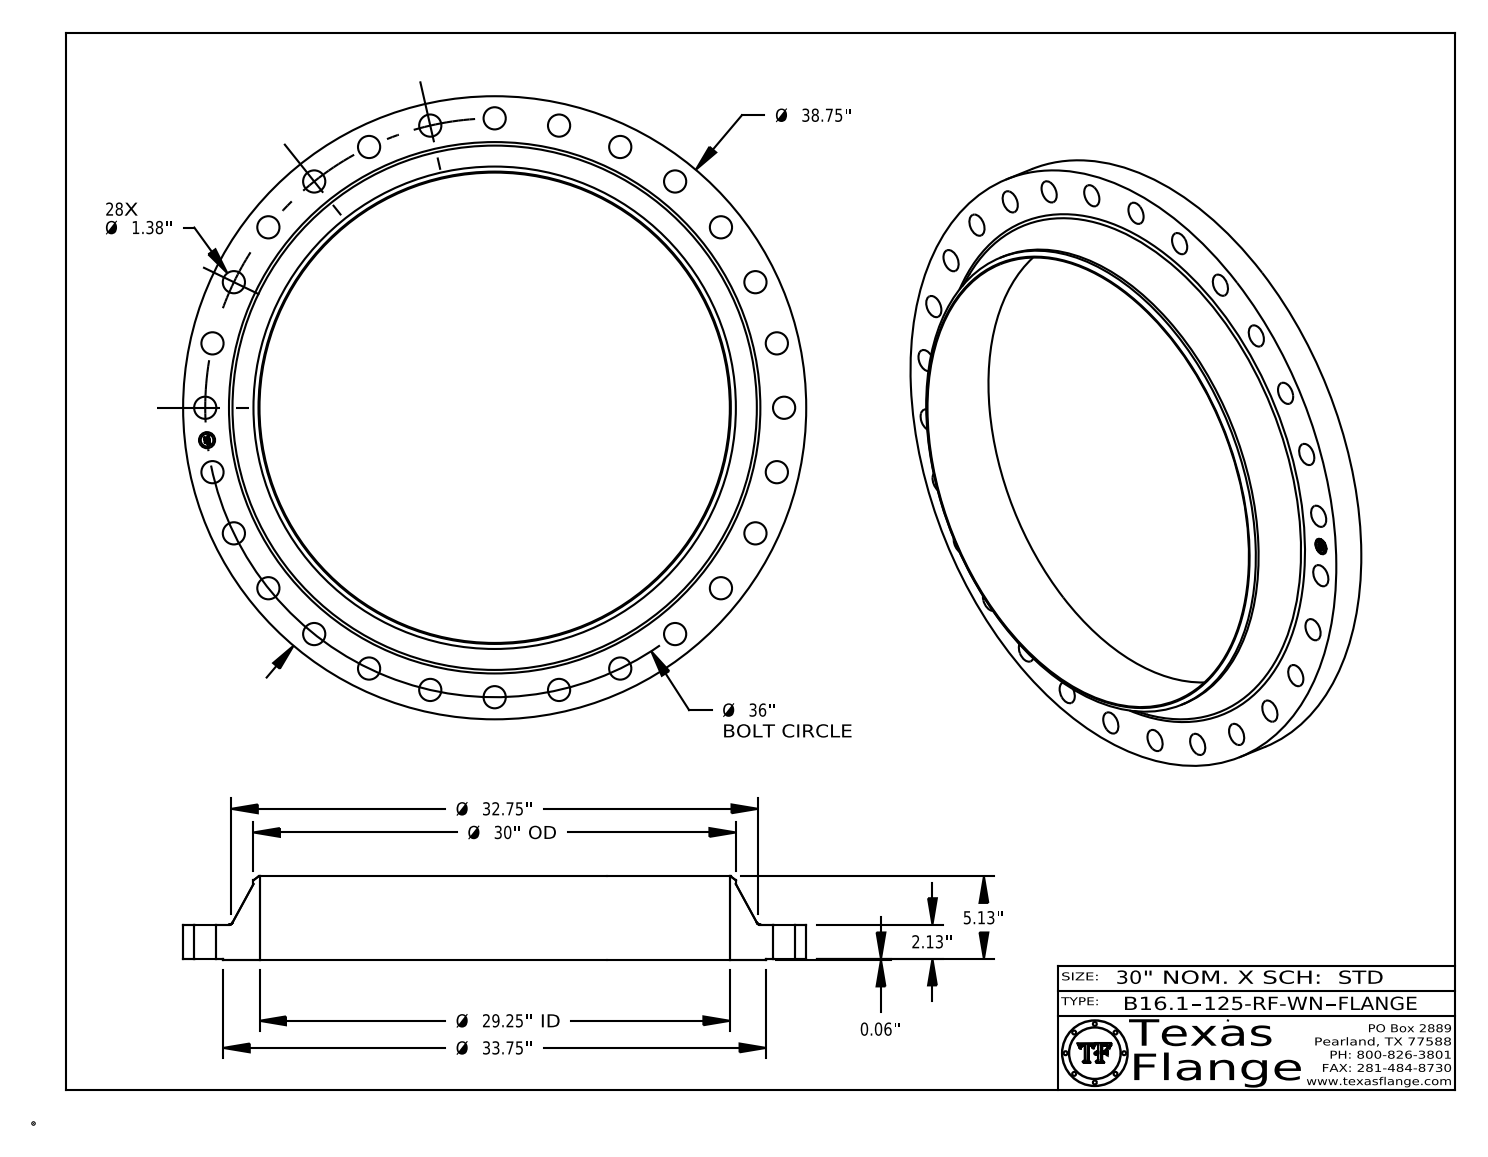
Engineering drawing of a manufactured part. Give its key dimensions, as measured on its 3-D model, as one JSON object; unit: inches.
{"part_name": "B16.1, Class 125-RF-WN", "step_written_by": "CATIA V5 STEP AP214 (AUTOMOTIVE_DESIGN)", "units": "inches", "bodies": {"solids": 1, "faces": 459, "planar": 369, "cylindrical": 84, "other": 6}, "overall_size": [38.75, 38.75, 5.193], "volume_in3": 1276, "surface_area_in2": 2108, "round_holes": [[1.38, 28], [1, 1], [29.25, 1]], "round_bosses_or_shafts": [[0.061, 8], [38.75, 1], [33.75, 1], [30, 1], [0.788, 1]], "face_to_face_distances": [2.13, 0.063, 2.193, 5.193, 5.13, 3, 0.015, 2.178, 2.115, 3.015], "hole_center_spacings": [18, 19.153, 4.031, 8.011, 11.89, 15.62, 22.446, 25.456]}
